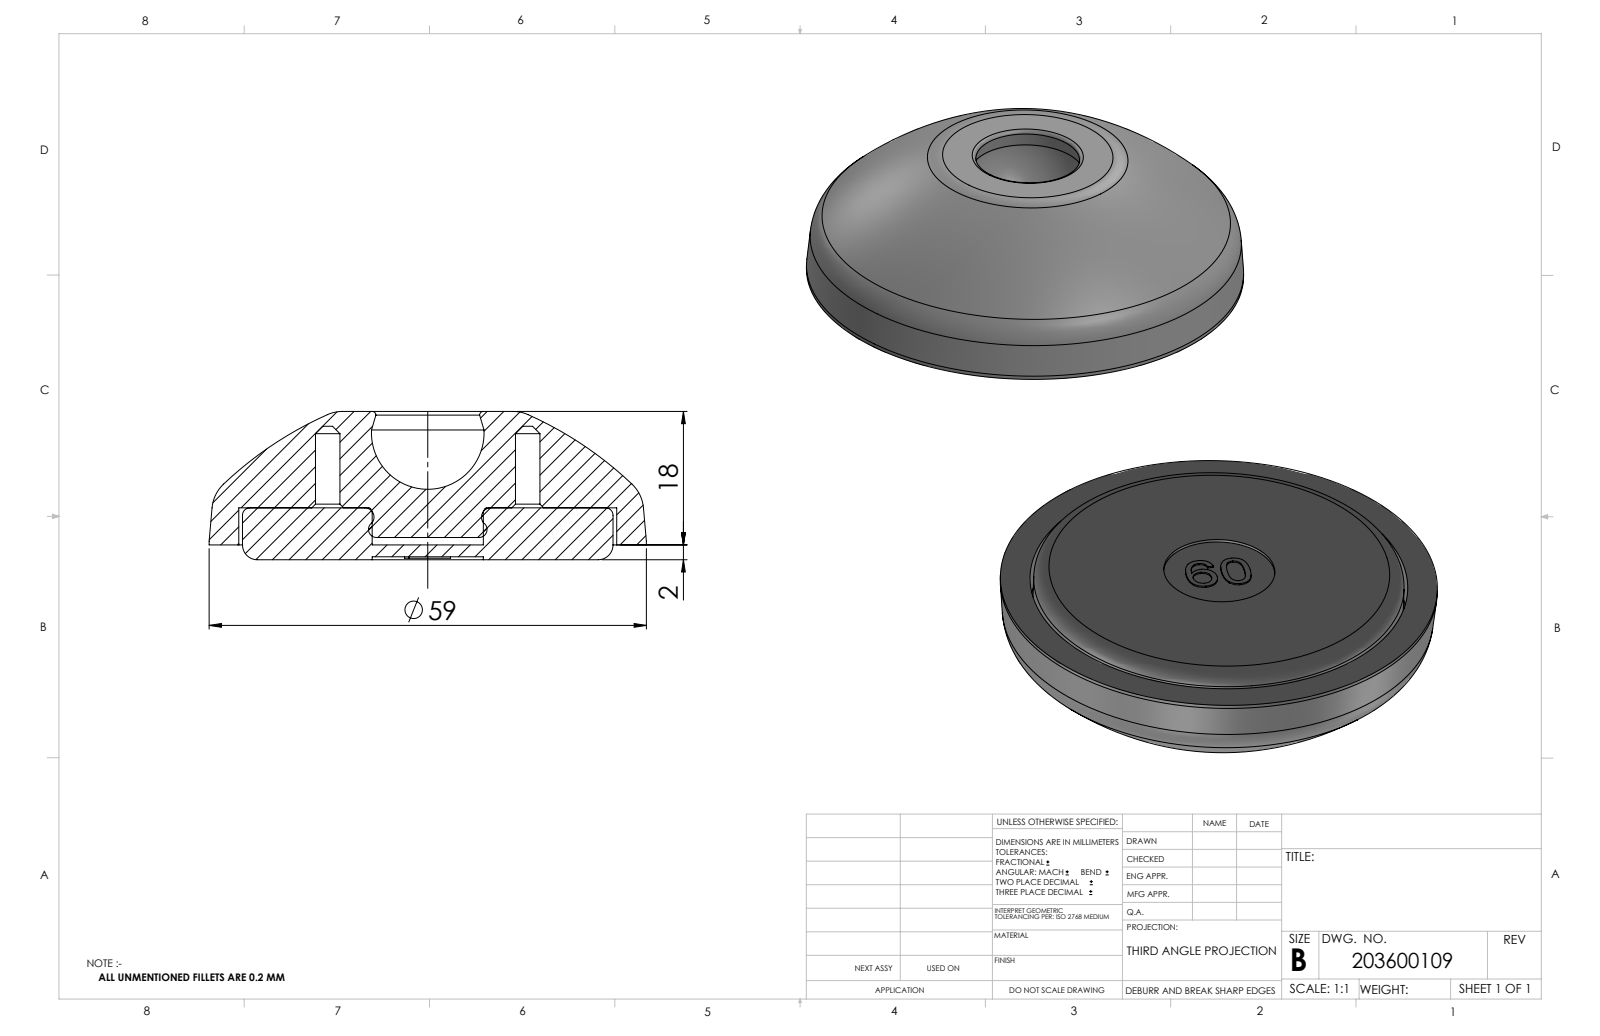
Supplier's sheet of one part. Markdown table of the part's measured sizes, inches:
| quantity | value |
| --- | --- |
| part name | 203600109_c_1 |
| STEP written by | SolidWorks 2014 (CONFIG_CONTROL_DESIGN) |
| units | inches |
| bodies | 2 solids, 200 faces (42 planar, 20 cylindrical, 138 other) |
| overall size | 2.323 × 2.323 × 0.875 |
| volume | 1.967 in³ |
| surface area | 23.91 in² |
| round holes (diameter × count) | 0.13 × 2, 0.591 × 1, 2.008 × 1 |
| round bosses / shafts (diameter × count) | 2.323 × 1, 1.969 × 1 |
| partial cylindrical surfaces (radius × count) | 0.118 × 2 |
| main face-to-face distances | 0.276, 0.079, 0.197, 0.157, 0.709, 0.787, 0.512, 0.016, 0.063, 0.26 |
| hole center spacings | 0.531, 0.531, 1.063 |
